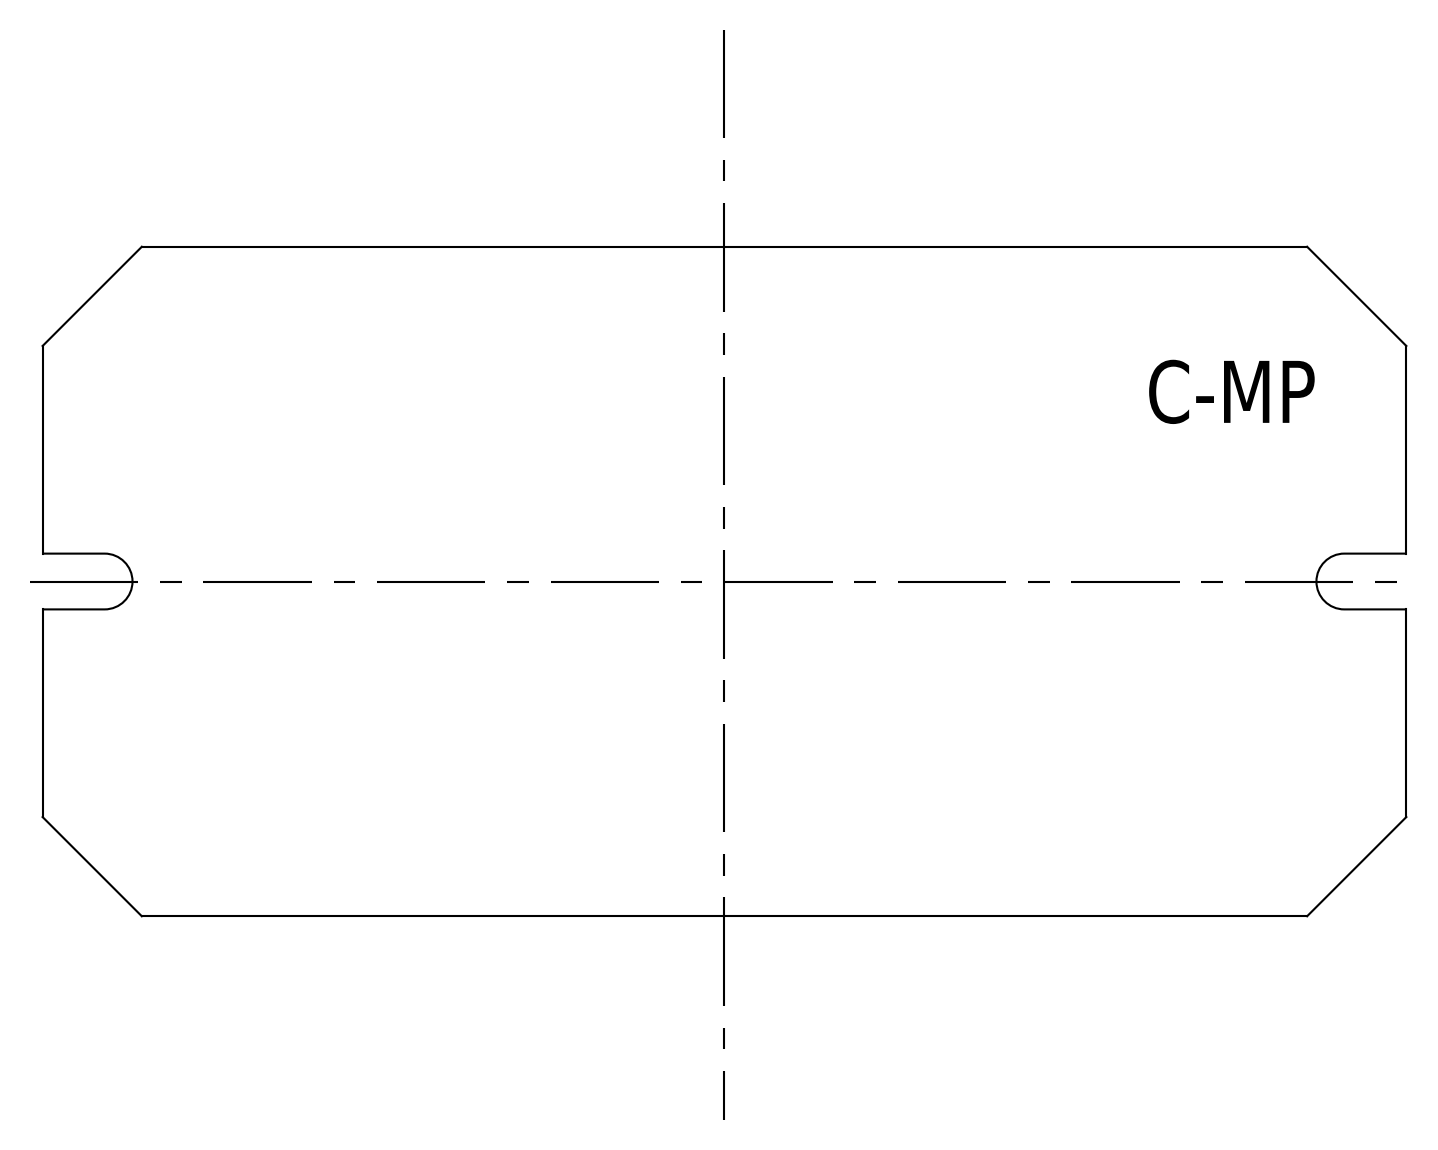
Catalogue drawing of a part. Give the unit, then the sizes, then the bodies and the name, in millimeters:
Units: millimetres
Overall size (bounding box): 110 × 54 × 1.5
Partial cylindrical surfaces — rounded edges, fillets, slot ends (radius × count): R2.25 ×2
Main face-to-face distances: 1.5, 54, 110, 104.64, 24.75, 29.25, 4.5
Volume: 8 627 mm³ · Surface area: 12 004 mm²
Bodies: 1 solid, 18 faces (16 planar, 2 cylindrical, 0 other)
Part name (STEP PRODUCT): C-MP
STEP written by: SolidWorks 2009 (AUTOMOTIVE_DESIGN)
